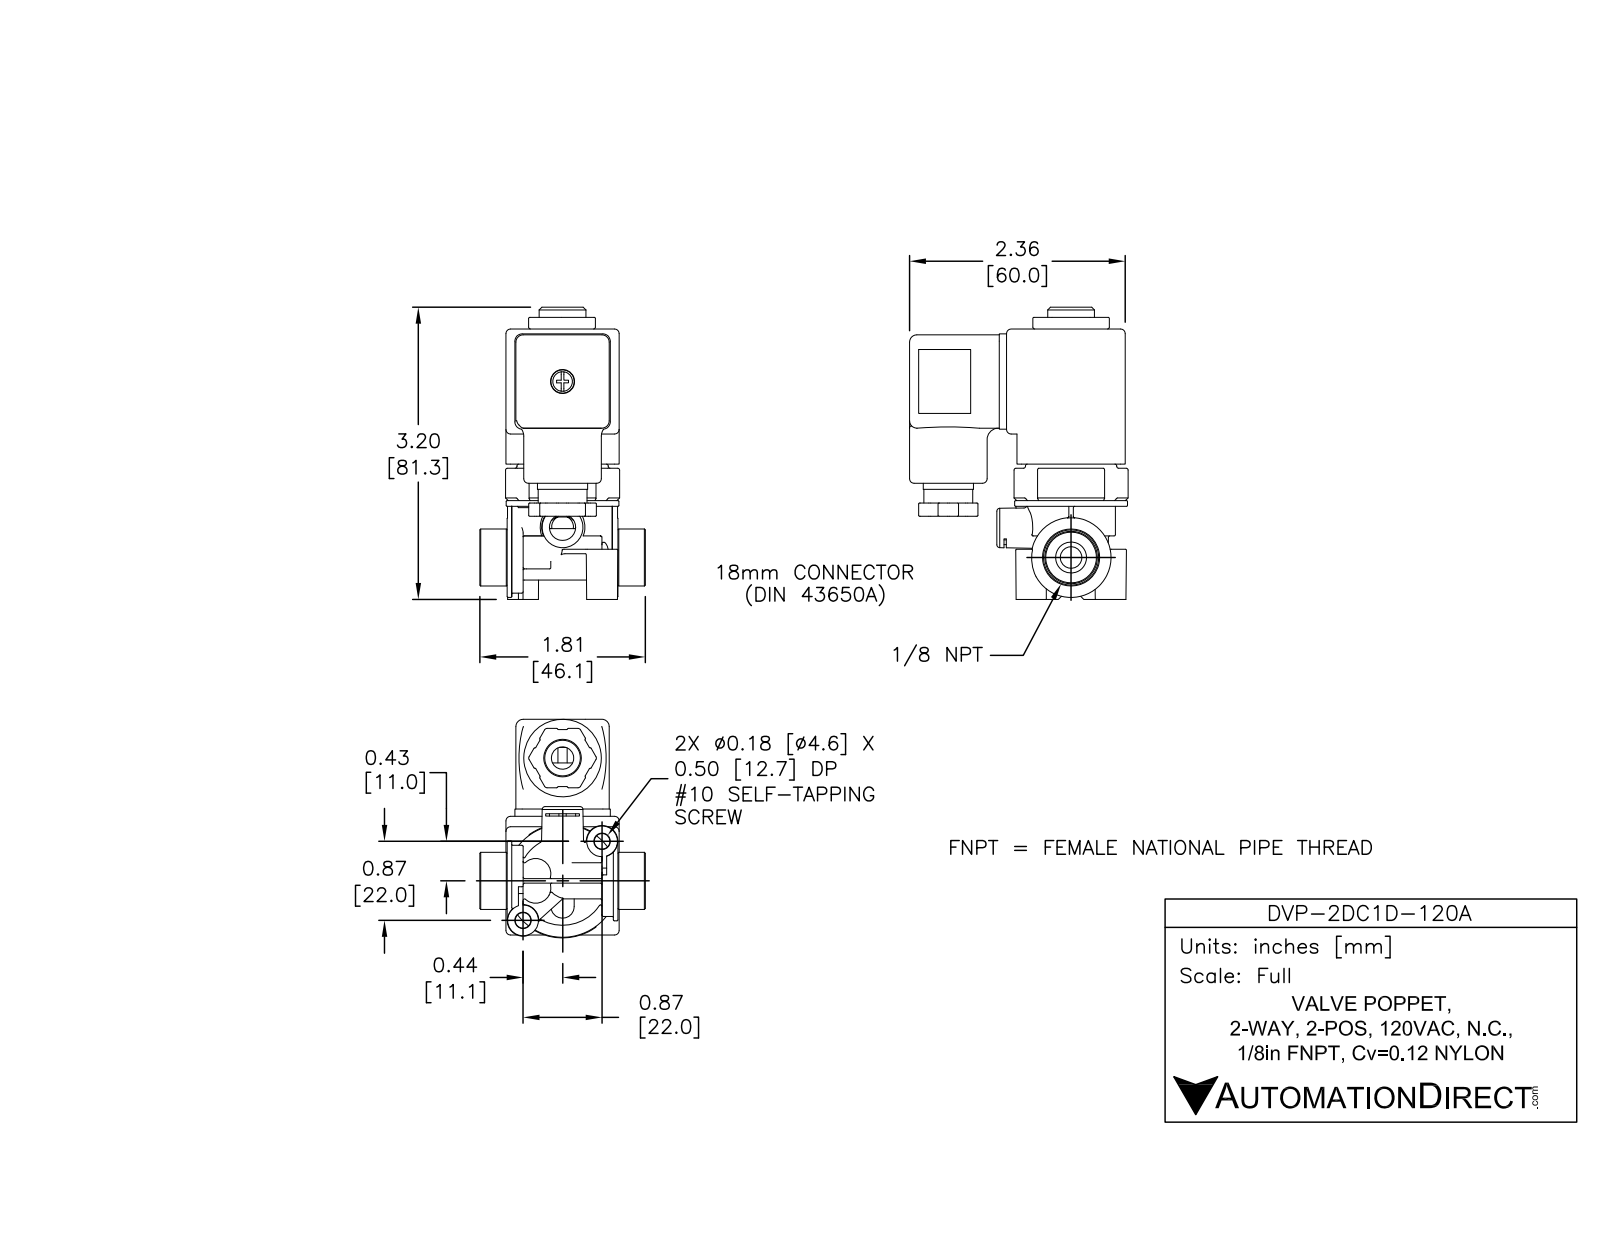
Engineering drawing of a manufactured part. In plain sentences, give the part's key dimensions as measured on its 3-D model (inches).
The part is named "DVP-2DC1D-120A". Its 3-D file was written by "SolidWorks 2015 (AUTOMOTIVE_DESIGN)". It is 9 solids with 2037 faces: 819 planar, 388 cylindrical and 830 other. Overall it measures 3.216 by 2.395 by 1.813 inches. Its volume is 4.043 cubic inches and its surface area 56.93 square inches. Round holes: 2 of diameter 0.06, 2 of diameter 0.236, 1 of diameter 0.08, 1 of diameter 0.102, 1 of diameter 0.12, 1 of diameter 0.203, 1 of diameter 0.245, 1 of diameter 0.263, 1 of diameter 0.287, 1 of diameter 0.339, 1 of diameter 0.37, 1 of diameter 0.375. Round bosses or shafts: 2 of diameter 0.29, 1 of diameter 1.236, 1 of diameter 1, 1 of diameter 0.972, 1 of diameter 0.922, 1 of diameter 0.89, 1 of diameter 0.875, 1 of diameter 0.85. Partial cylindrical surfaces (rounded edges, fillets, slot ends): 85 of radius 0.01, 50 of radius 0.015, 21 of radius 0.05, 12 of radius 0.02, 12 of radius 0.08, 6 of radius 0.026, 6 of radius 0.03, 4 of radius 0.04. The main face-to-face distances are 1.083, 1.24, 0.048, 0.157, 0.925, 1.48, 0.109, 1.131, 0.974, 1.367. The hole center spacings are 0.281, 0.283, 1.062, 1.343, 1.345, 1.612, 1.626, 2.184.
